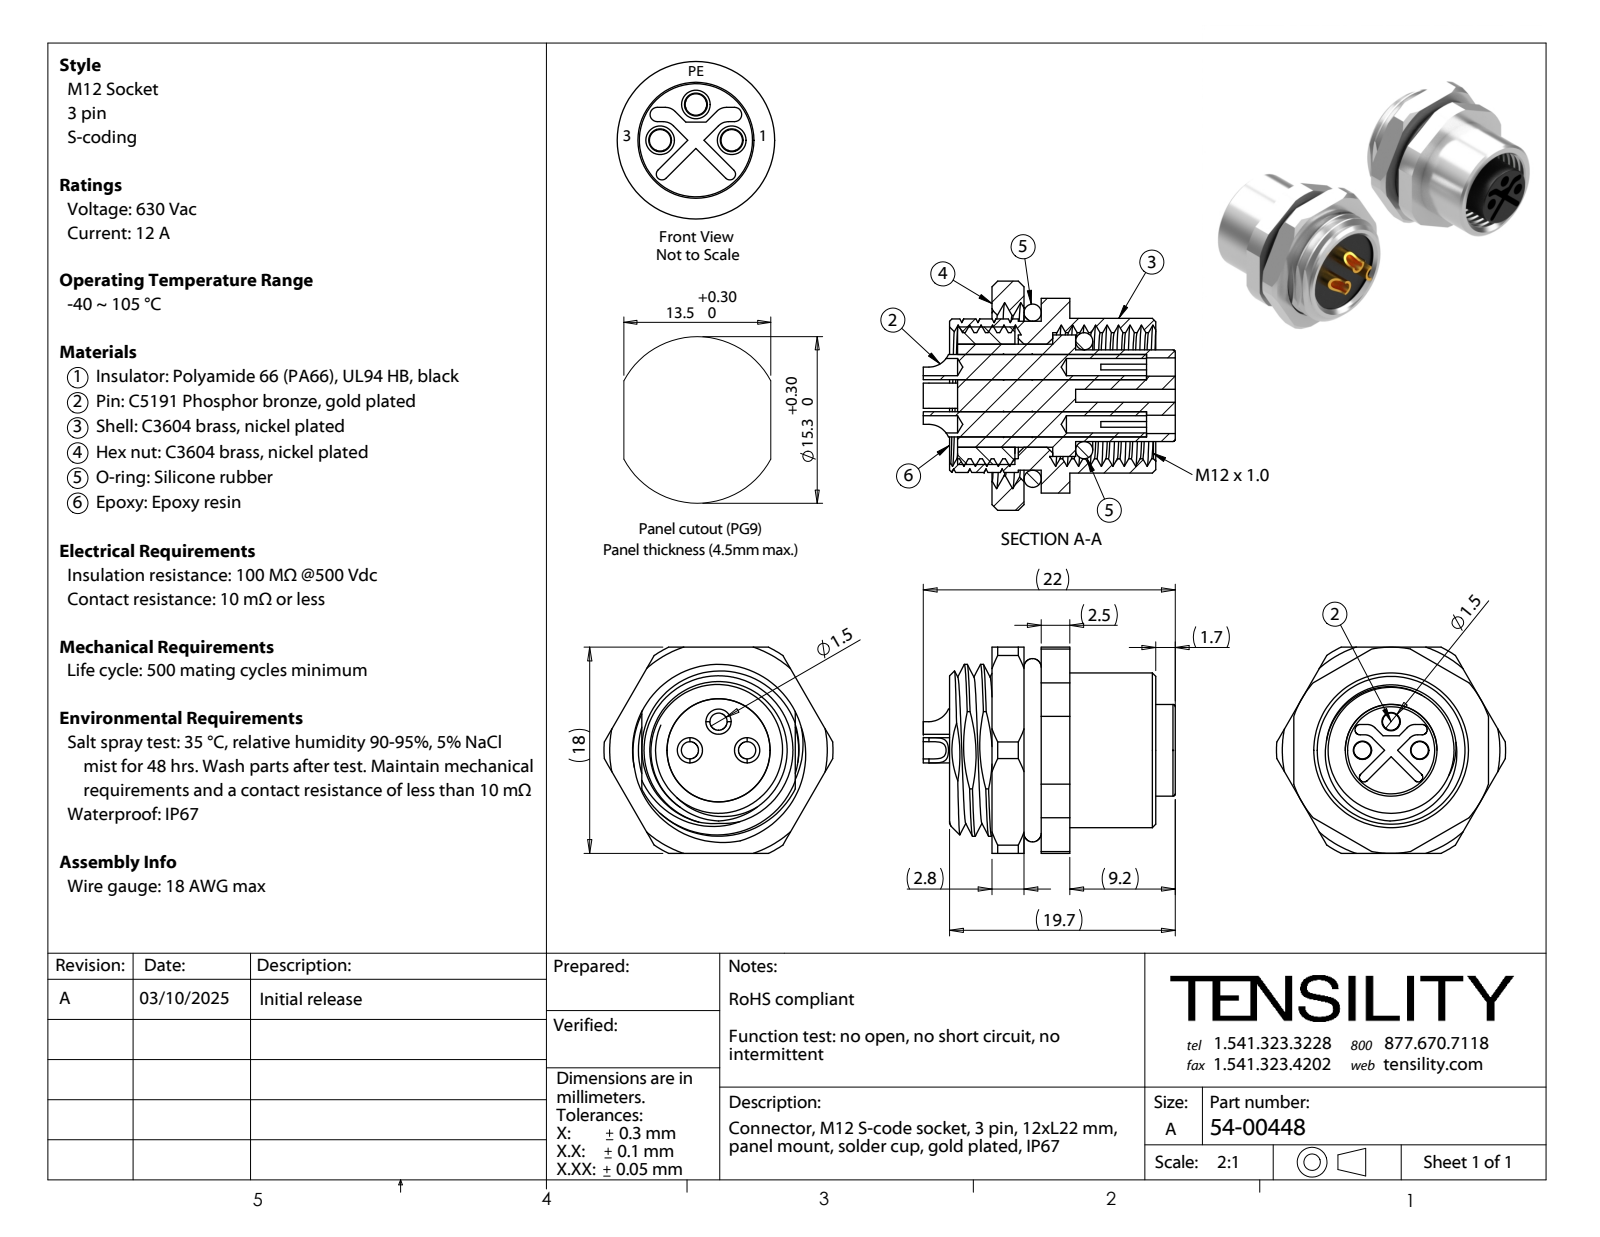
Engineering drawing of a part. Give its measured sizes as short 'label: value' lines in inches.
name: 54-00448-04; 54-00448-06; 54-00448-02; 54-00448-05 (+3 more)
written by: SolidWorks 2021 (CONFIG_CONTROL_DESIGN)
unit: in
bodies: 9 solids, 301 faces (95 planar, 130 cylindrical, 76 other)
size: 0.866 × 0.787 × 0.709
volume: 0.167 in³; area: 8.795 in²
holes: 3× ⌀0.059, 3× ⌀0.063, 1× ⌀0.354, 1× ⌀0.433, 1× ⌀0.551
bosses: 3× ⌀0.087, 1× ⌀0.531, 1× ⌀0.512, 1× ⌀0.472, 1× ⌀0.417, 1× ⌀0.315
rounds: 4× R0.039, 3× R0.073, 2× R0.016, 2× R0.018, 1× R0.295, 1× R0.354, 1× R0.394
face distances: 0.118, 0.287, 0.098, 0.031, 0.209, 0.079, 0.059, 0.386, 0.02, 0.197
hole spacings: 0.098, 0.139, 0.197
